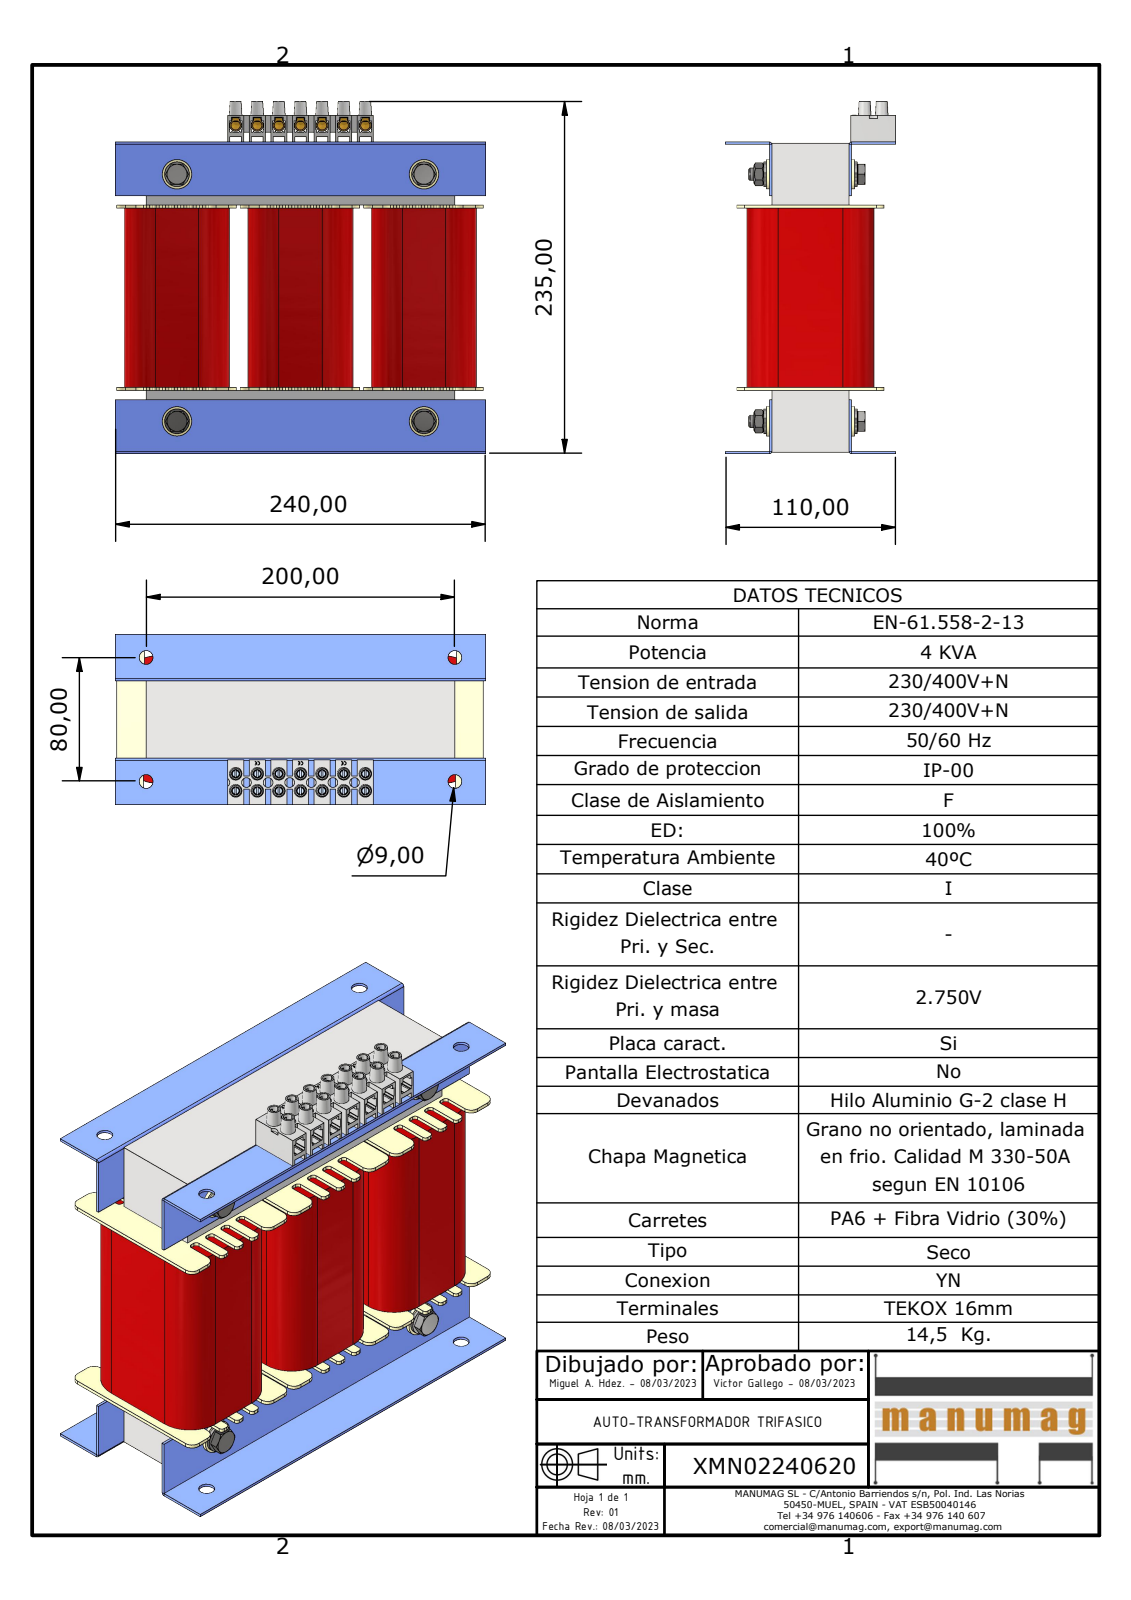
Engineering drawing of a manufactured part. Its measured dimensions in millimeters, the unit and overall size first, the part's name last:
Units: millimetres
Overall size (bounding box): 240 × 228.3 × 110
Round holes (diameter × count): ⌀3.24 ×14, ⌀5.5 ×14, ⌀6 ×7, ⌀6.3 ×6, ⌀6.65 ×4, ⌀8 ×4, ⌀8.4 ×4, ⌀9 ×4, ⌀10.5 ×4, ⌀11 ×4
Round bosses / shafts (diameter × count): ⌀4 ×14, ⌀19 ×4, ⌀16 ×4, ⌀11.4 ×4, ⌀9.6 ×4, ⌀7.32 ×4
Partial cylindrical surfaces — rounded edges, fillets, slot ends (radius × count): R2 ×84, R2.75 ×28, R5 ×24, R0.82 ×16, R3 ×14, R20 ×12, R0.22 ×9, R0.81 ×8
Main face-to-face distances: 40, 80, 1.5, 50, 160, 120, 66, 51.5, 14, 54
Hole centre spacings: 14, 28, 42, 8.8, 9, 17.8, 56, 21.67
Volume: 2 817 000 mm³ · Surface area: 528 245 mm²
Bodies: 68 solids, 3127 faces (2119 planar, 547 cylindrical, 461 other)
Part name (STEP PRODUCT): XMN02240620; 3UI120 200 x 200 - 50 (Rc40); UI 120_50; RC40 NT040 (+8 more)
STEP written by: Autodesk Inventor 2023 (AUTOMOTIVE_DESIGN)
